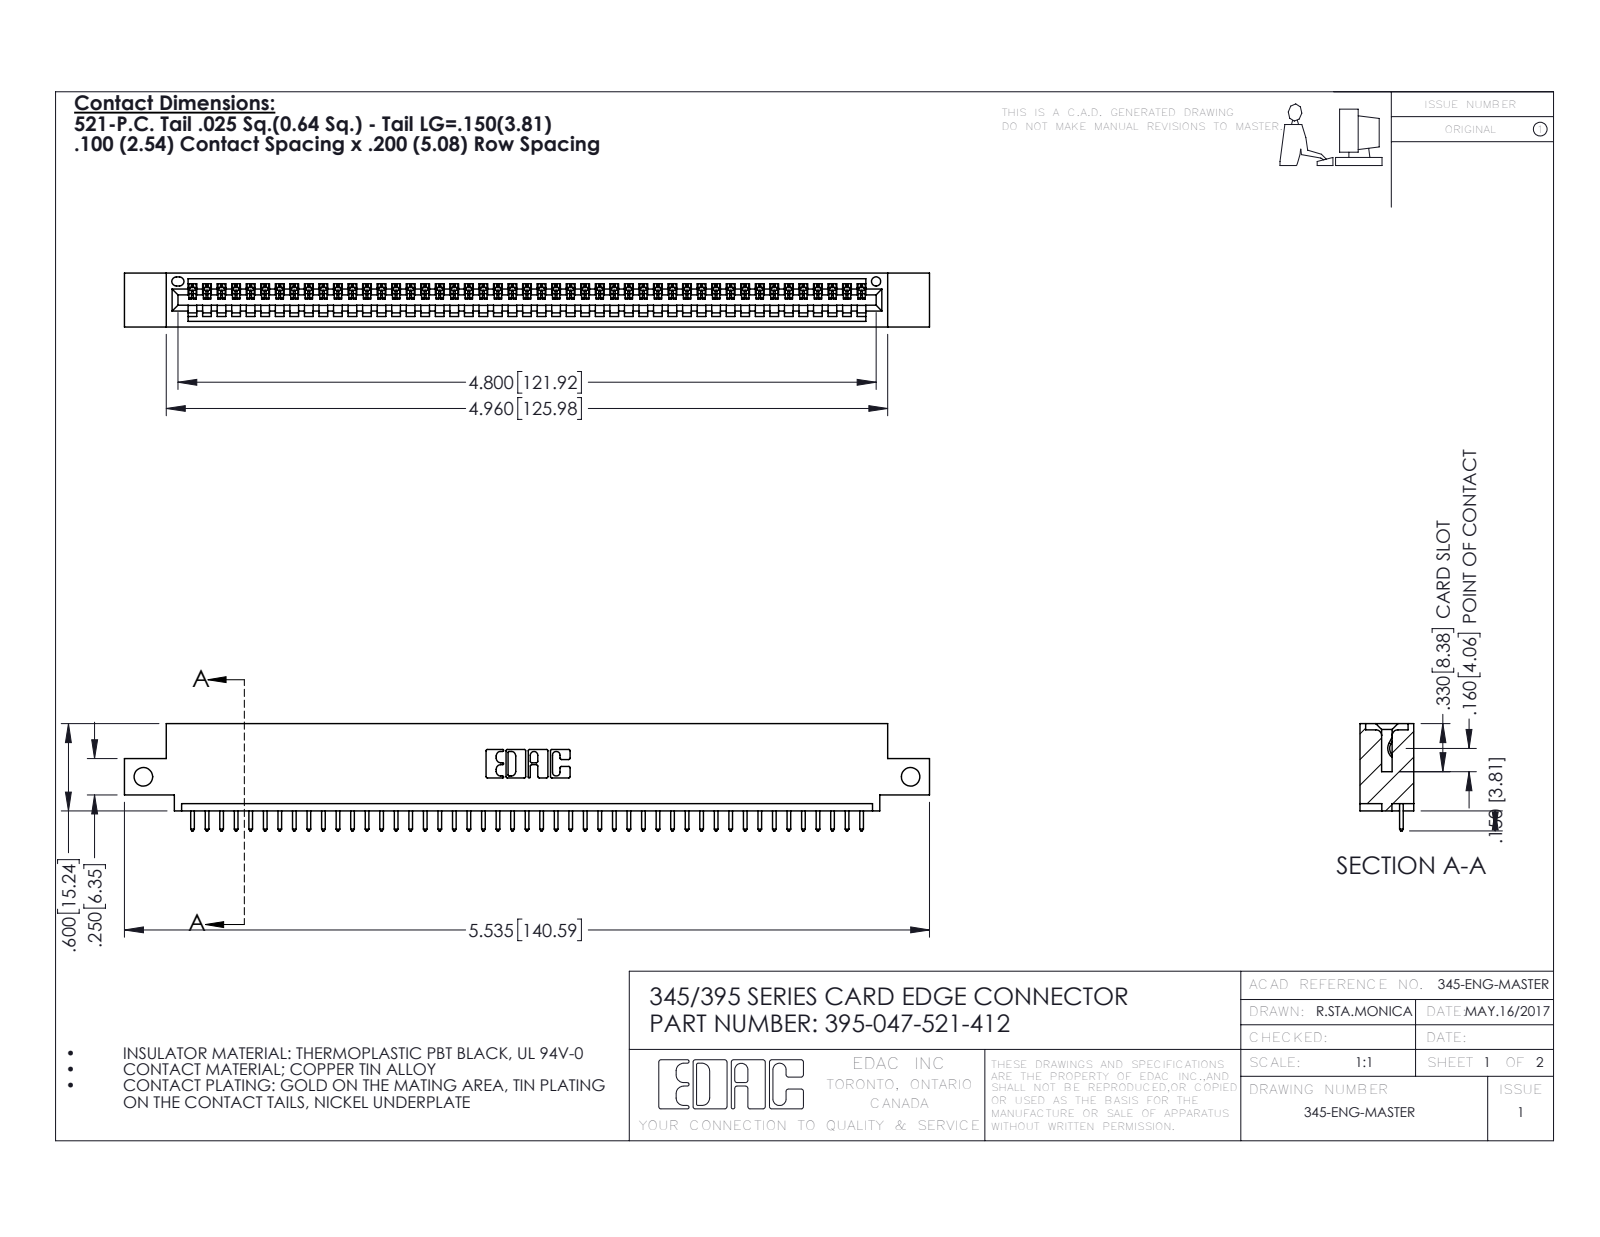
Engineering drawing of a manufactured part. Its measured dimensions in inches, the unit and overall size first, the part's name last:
Units: inches
Overall size (bounding box): 5.535 × 0.737 × 0.37
Round holes (diameter × count): ⌀0.128 ×2, ⌀0.064 ×1
Partial cylindrical surfaces — rounded edges, fillets, slot ends (radius × count): R0.006 ×94, R0.01 ×94, R0.01 ×22, R0.007 ×6, R0.031 ×6, R0.026 ×3, R0.031 ×2, R0.04 ×2
Main face-to-face distances: 0.072, 0.298, 0.37, 0.2, 0.098, 0.272, 0.025, 0.225, 0.149, 0.072
Hole centre spacings: 5.275
Volume: 0.799 in³ · Surface area: 26.18 in²
Bodies: 48 solids, 2856 faces (1964 planar, 892 cylindrical, 0 other)
Part name (STEP PRODUCT): 395-047-521-412; 345 Part_0.110 Offset - Side Mount; 345-292-001_345-293-121
STEP written by: SolidWorks 2016 (CONFIG_CONTROL_DESIGN)
